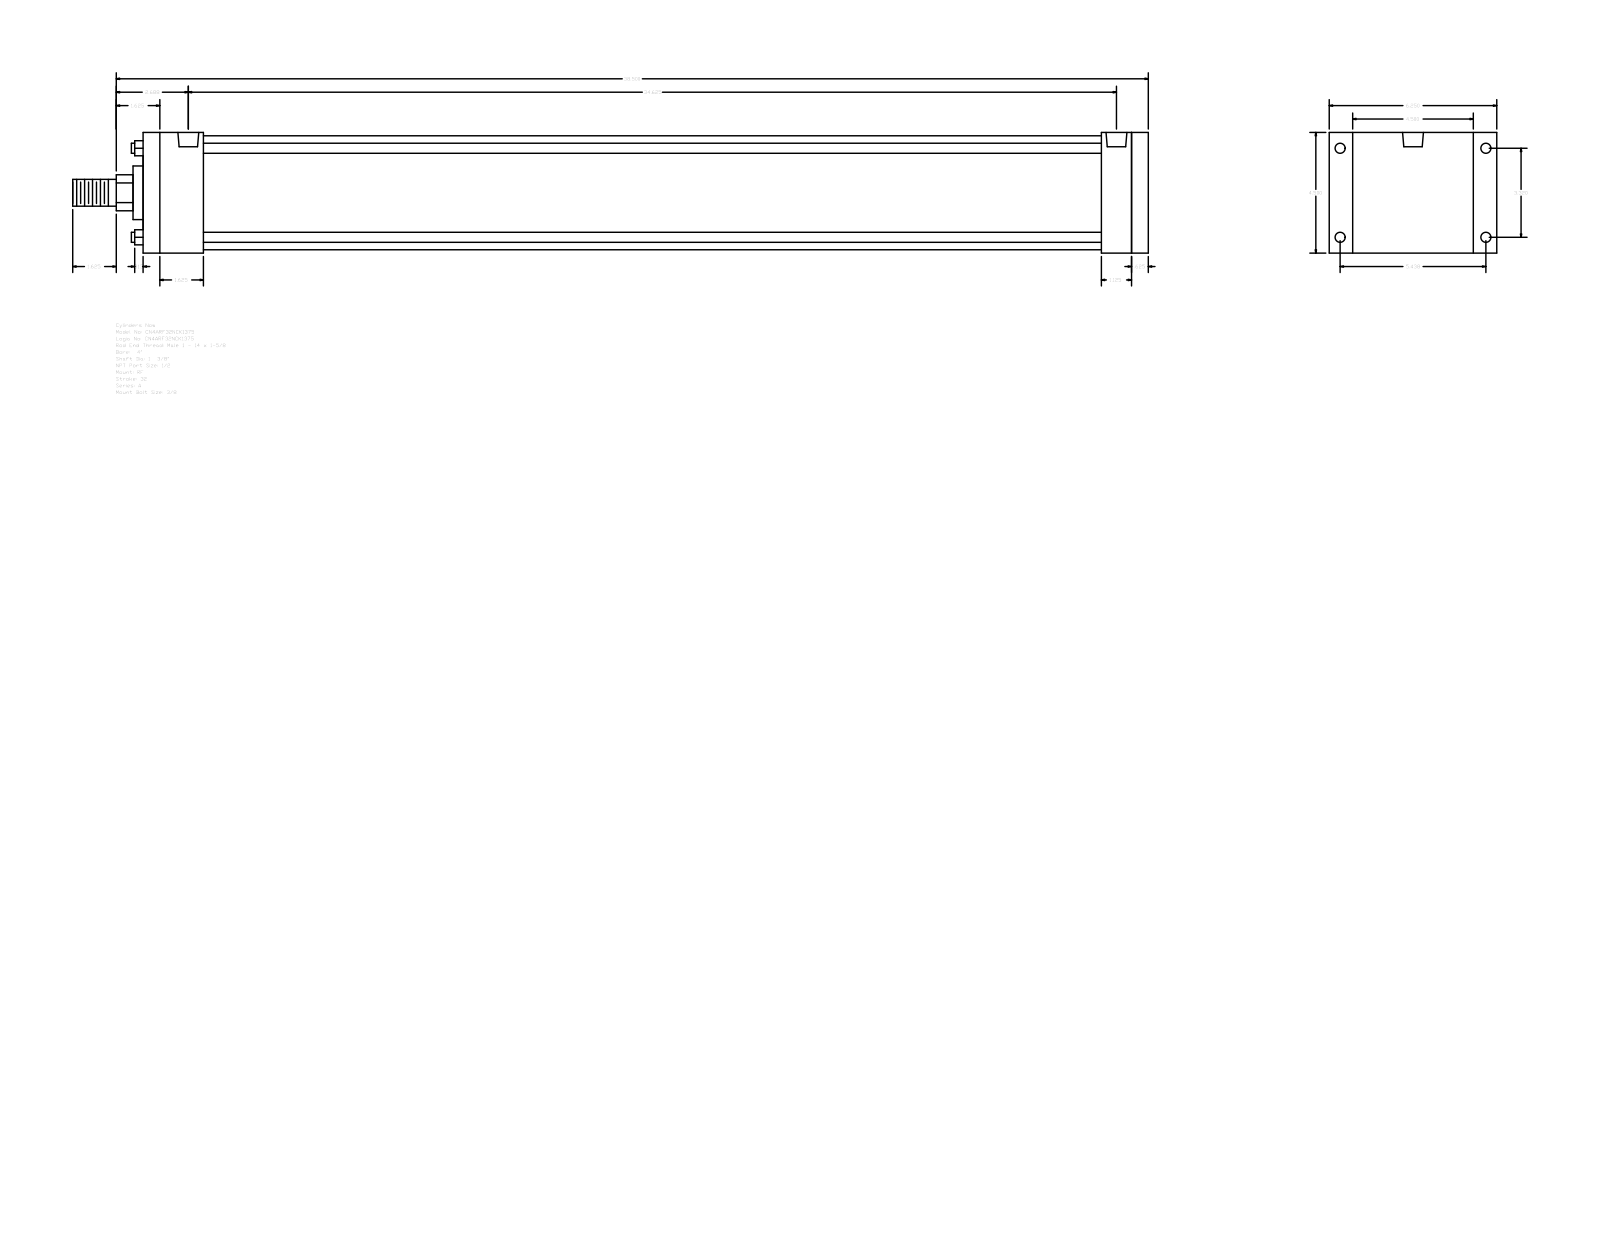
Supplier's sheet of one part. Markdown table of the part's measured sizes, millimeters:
| quantity | value |
| --- | --- |
| part name | A_RF__0400_1.375 |
| STEP written by | GSSL Pune (CONFIG_CONTROL_DESIGN) |
| units | millimeters |
| bodies | 0 solids, 92 faces (64 planar, 28 cylindrical, 0 other) |
| overall size | 1019.17 × 158.75 × 114.3 |
| round holes (diameter × count) | 8.73 × 4, 9.53 × 4, 19.77 × 2 |
| round bosses / shafts (diameter × count) | 9.53 × 4, 107.95 × 1, 50.8 × 1, 34.92 × 1, 25.4 × 1 |
| partial cylindrical surfaces (radius × count) | 17.06 × 1 |
| main face-to-face distances | 114.3, 952.5, 15.88, 936.62, 57.15, 22.23, 136.53, 908.05, 28.57, 44.45 |
| hole center spacings | 3.18, 84.32, 138.12, 161.82, 873.12, 876.3, 879.48 |
